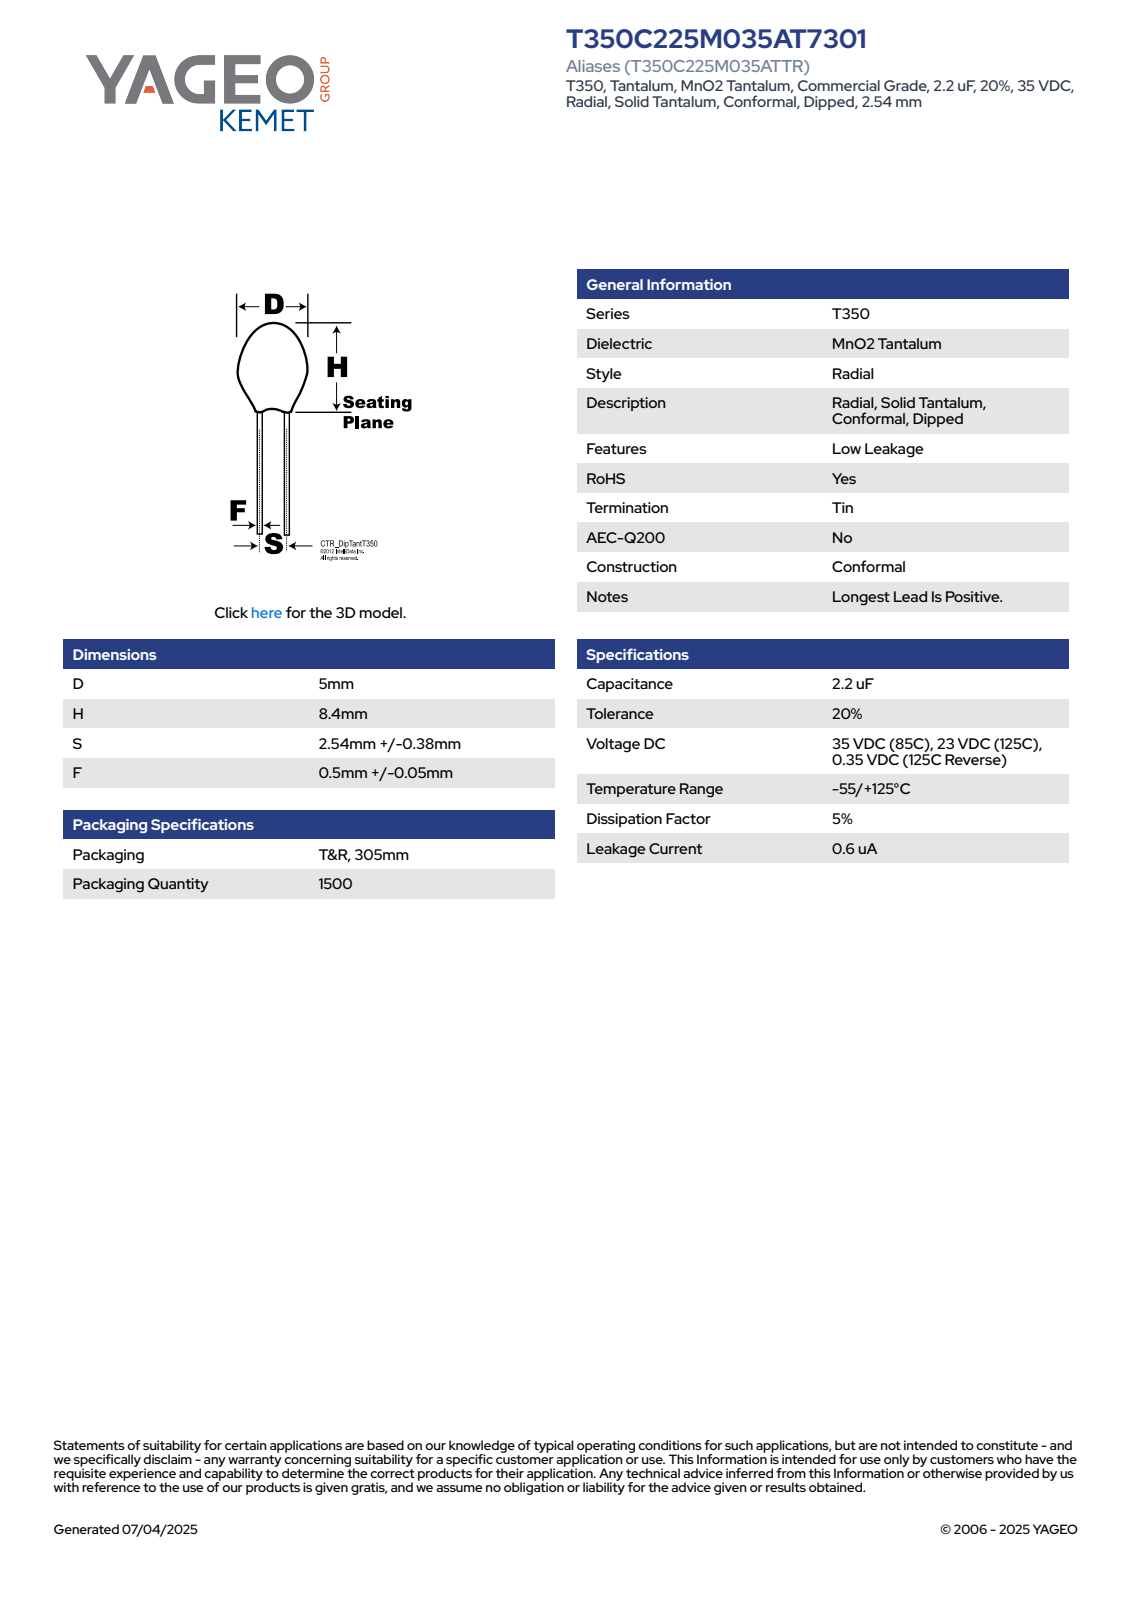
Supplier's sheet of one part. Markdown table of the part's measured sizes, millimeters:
| quantity | value |
| --- | --- |
| part name | CTR_T350_D5H8.4S2.54LL13.96F0.55 |
| STEP written by | SolidWorks 2014 (AUTOMOTIVE_DESIGN) |
| units | millimeters |
| bodies | 1 solid, 73 faces (26 planar, 10 cylindrical, 37 other) |
| overall size | 22.36 × 5 × 5 |
| volume | 146 mm³ |
| surface area | 190 mm² |
| round bosses / shafts (diameter × count) | 0.55 × 2, 5 × 1 |
| partial cylindrical surfaces (radius × count) | 2.49 × 1 |
| main face-to-face distances | 8.4, 13.96, 22.36, 18.58, 4.62, 3.78, 17.78, 3.82, 0.8, 4.58 |
